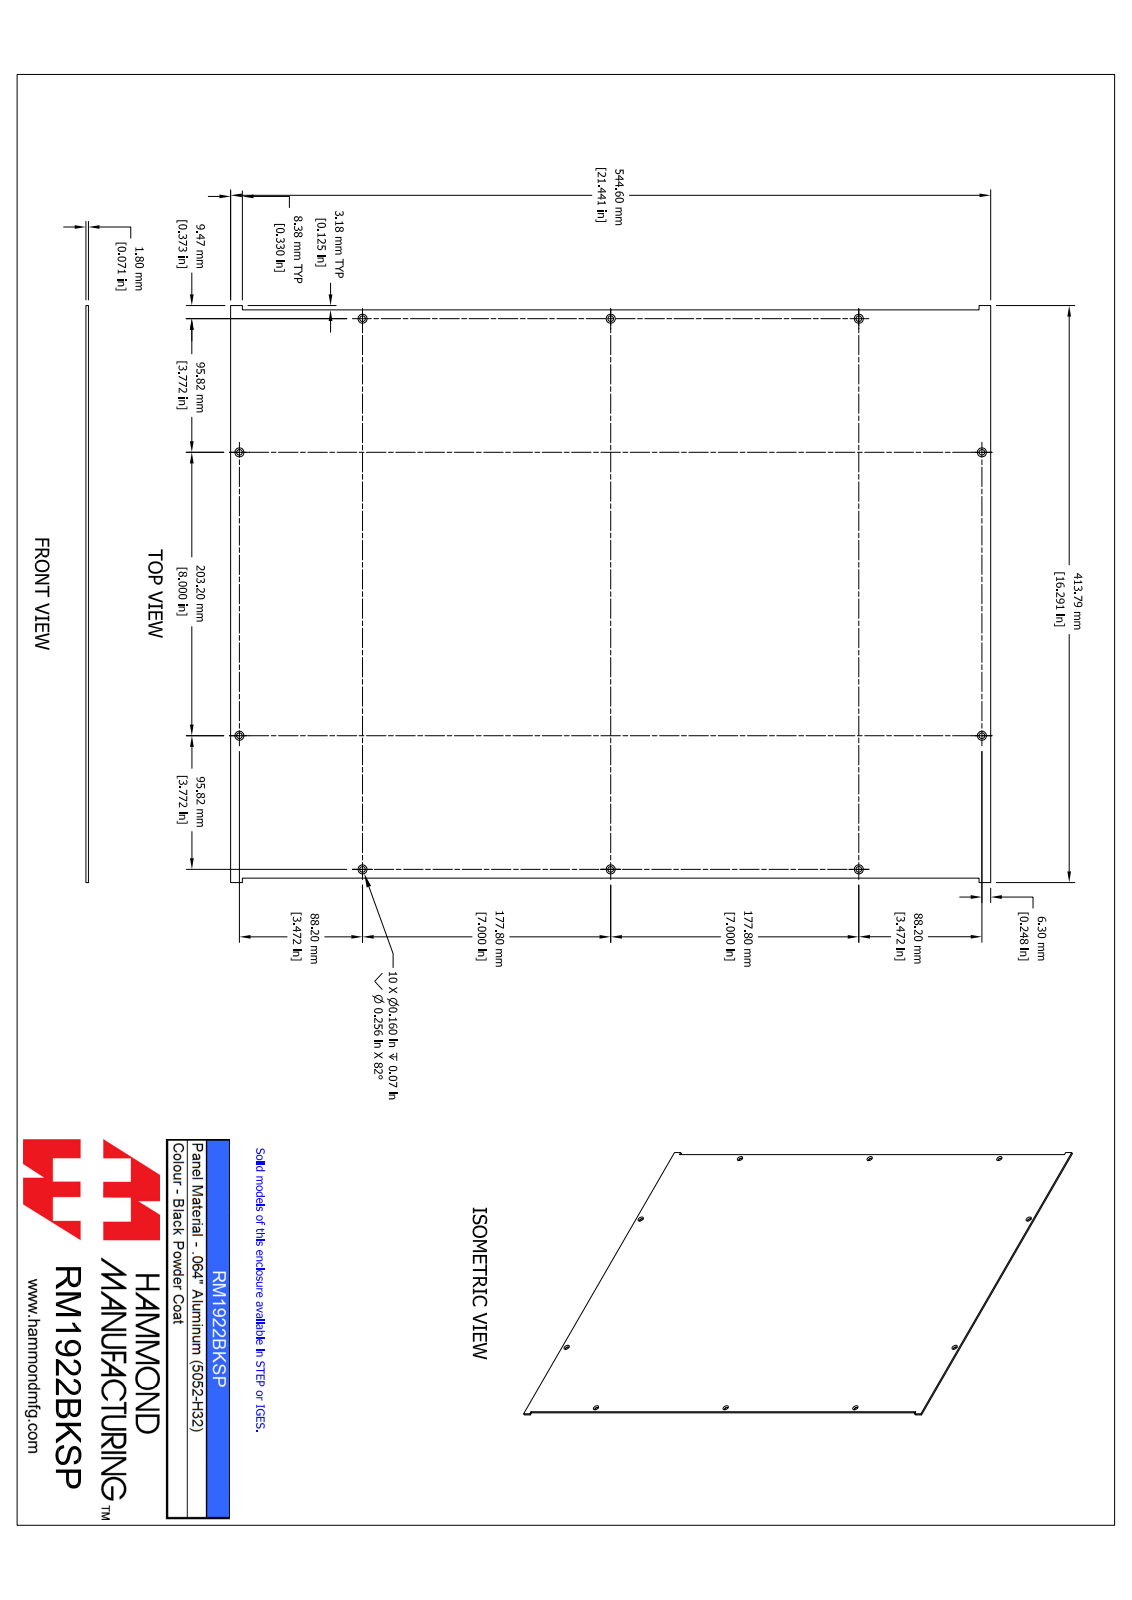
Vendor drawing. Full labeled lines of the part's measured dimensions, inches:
Part name (STEP PRODUCT): RM1922BKSP
STEP written by: SolidWorks 2021 (AUTOMOTIVE_DESIGN)
Units: inches
Bodies: 1 solid, 34 faces (14 planar, 10 cylindrical, 10 other)
Overall size (bounding box): 21.441 × 16.291 × 0.071
Volume: 24.41 in³ · Surface area: 693.4 in²
Round holes (diameter × count): ⌀0.16 ×10
Main face-to-face distances: 0.071, 16.041, 21.441, 0.125, 16.166, 16.291, 0.33, 21.111, 20.781
Hole centre spacings: 5.127, 7, 11.131, 12.274, 15.756, 17.048, 17.875, 21.069
